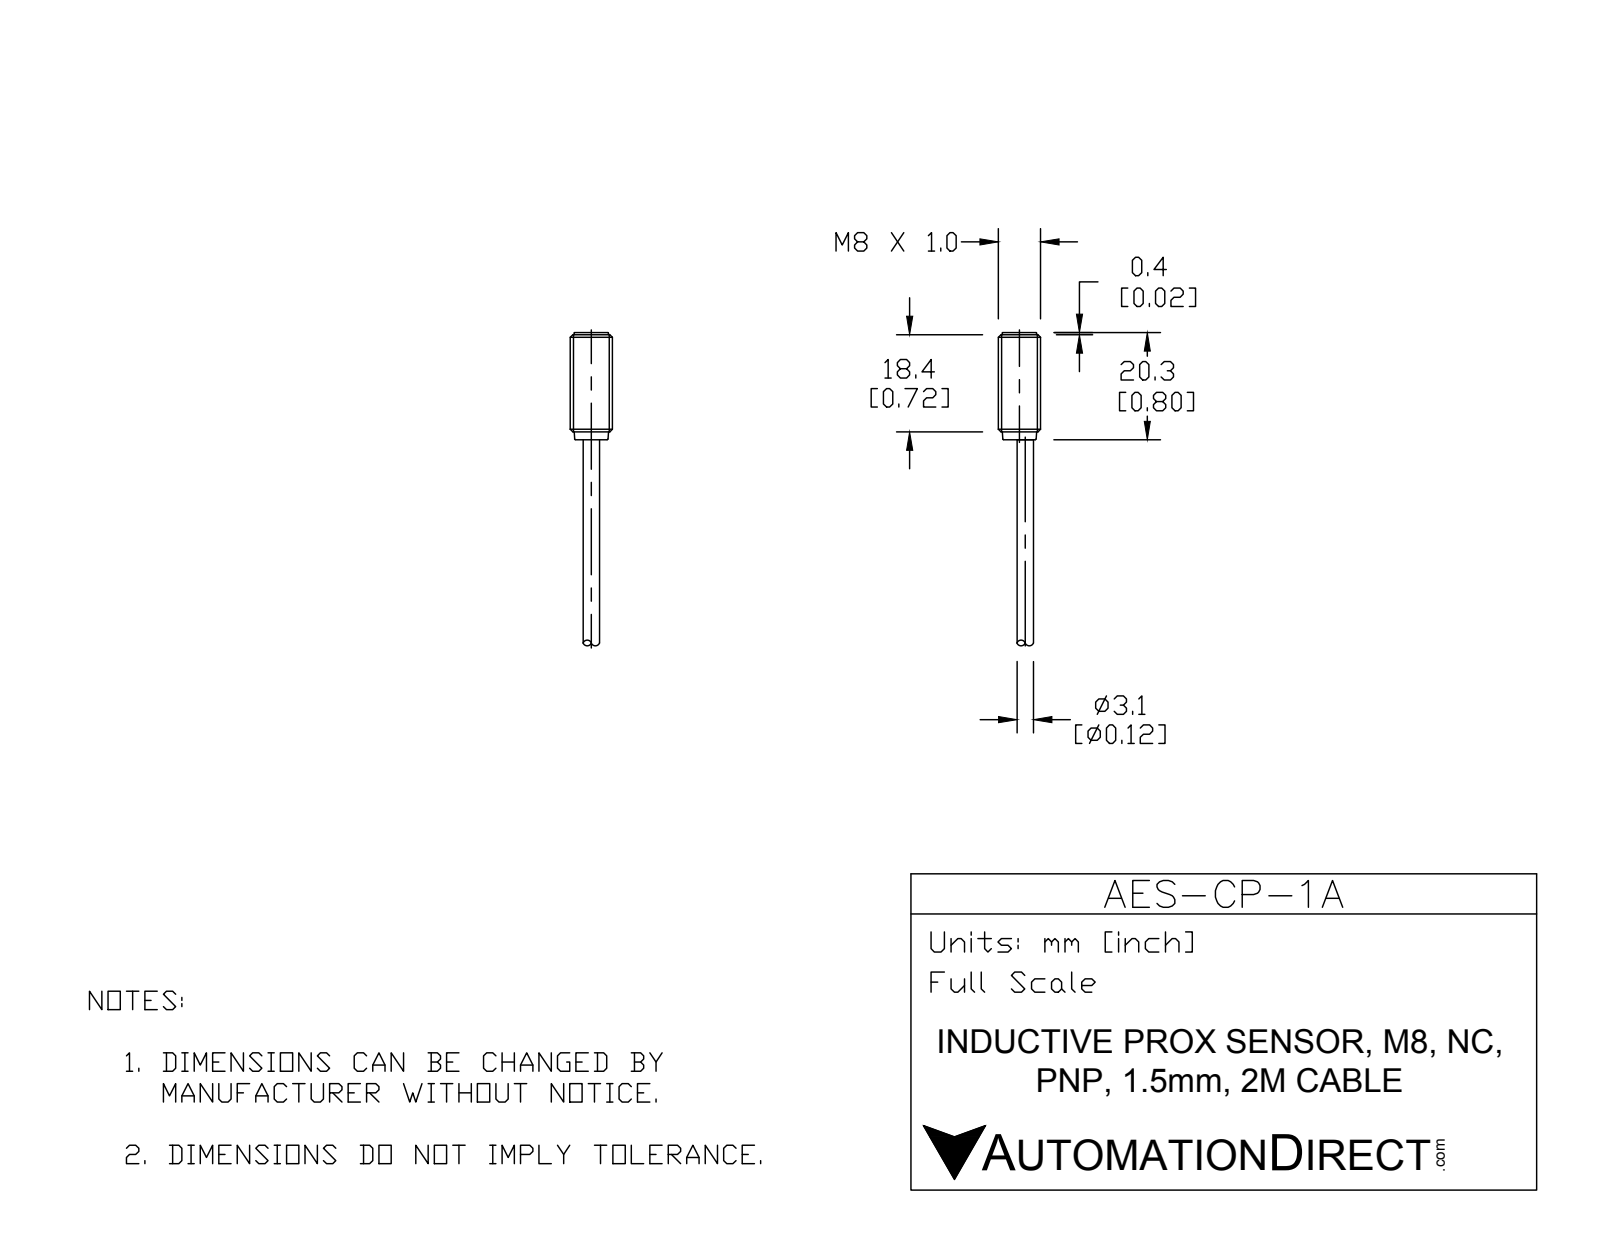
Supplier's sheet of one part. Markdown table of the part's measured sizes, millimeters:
| quantity | value |
| --- | --- |
| part name | AES-CP-1A |
| STEP written by | SolidWorks 2015 (CONFIG_CONTROL_DESIGN) |
| units | millimeters |
| bodies | 1 solid, 21 faces (5 planar, 6 cylindrical, 10 other) |
| overall size | 69.9 × 8 × 8 |
| volume | 1 335 mm³ |
| surface area | 1 054 mm² |
| round bosses / shafts (diameter × count) | 8 × 1, 6.5 × 1, 3.1 × 1 |
| main face-to-face distances | 19.9, 50, 69.9, 69.5, 19.5, 0.4, 51.5, 1.5, 18, 18.4 |
